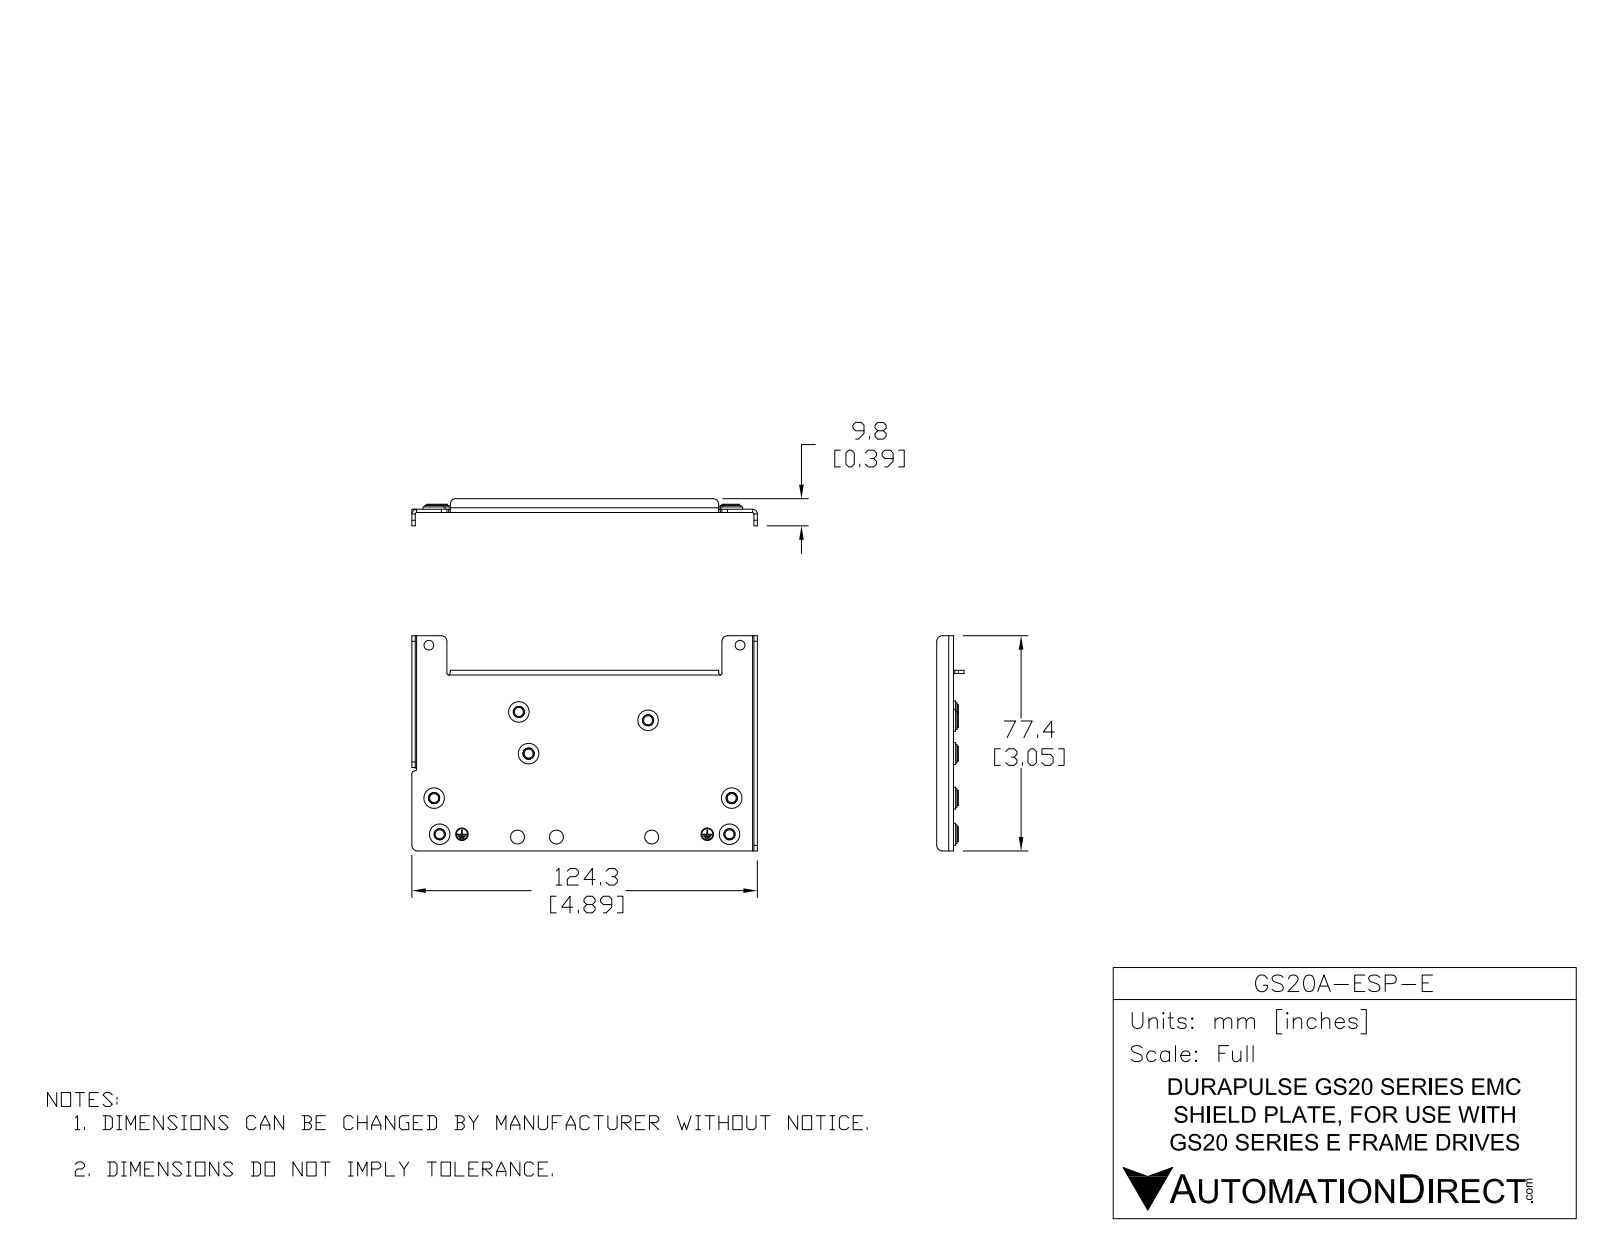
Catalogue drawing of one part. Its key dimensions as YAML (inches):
part_name: "MKM-EPE-PD-3D00 r1"
step_written_by: "SolidWorks 2017 (AUTOMOTIVE_DESIGN)"
units: inches
bodies: {solids: 15, faces: 618, planar: 233, cylindrical: 163, other: 222}
overall_size: [4.894, 3.047, 1.258]
volume: 1.171
surface_area: 56.21
round_holes:
  - {diameter: 0.128, count: 7}
  - {diameter: 0.213, count: 7}
  - {diameter: 0.213, count: 5}
  - {diameter: 0.197, count: 3}
  - {diameter: 0.138, count: 2}
  - {diameter: 0.315, count: 2}
round_bosses_or_shafts:
  - {diameter: 0.31, count: 7}
  - {diameter: 0.212, count: 7}
  - {diameter: 0.261, count: 4}
  - {diameter: 0.261, count: 3}
  - {diameter: 0.315, count: 2}
  - {diameter: 0.283, count: 2}
  - {diameter: 0.272, count: 2}
  - {diameter: 0.157, count: 2}
partial_cylinders:
  - {radius: 0.106, count: 10}
  - {radius: 0.295, count: 10}
  - {radius: 0.02, count: 8}
  - {radius: 0.079, count: 8}
  - {radius: 0.337, count: 5}
  - {radius: 0.376, count: 5}
  - {radius: 0.067, count: 3}
  - {radius: 0.039, count: 1}
face_to_face_distances: [0.047, 0.039, 0.087, 1.516, 0.846, 0.669, 1.508, 0.63, 0.886, 1.469]
hole_center_spacings: [0.354, 0.749, 1.103, 2.65, 2.681, 3.004, 3.752, 0.513]
